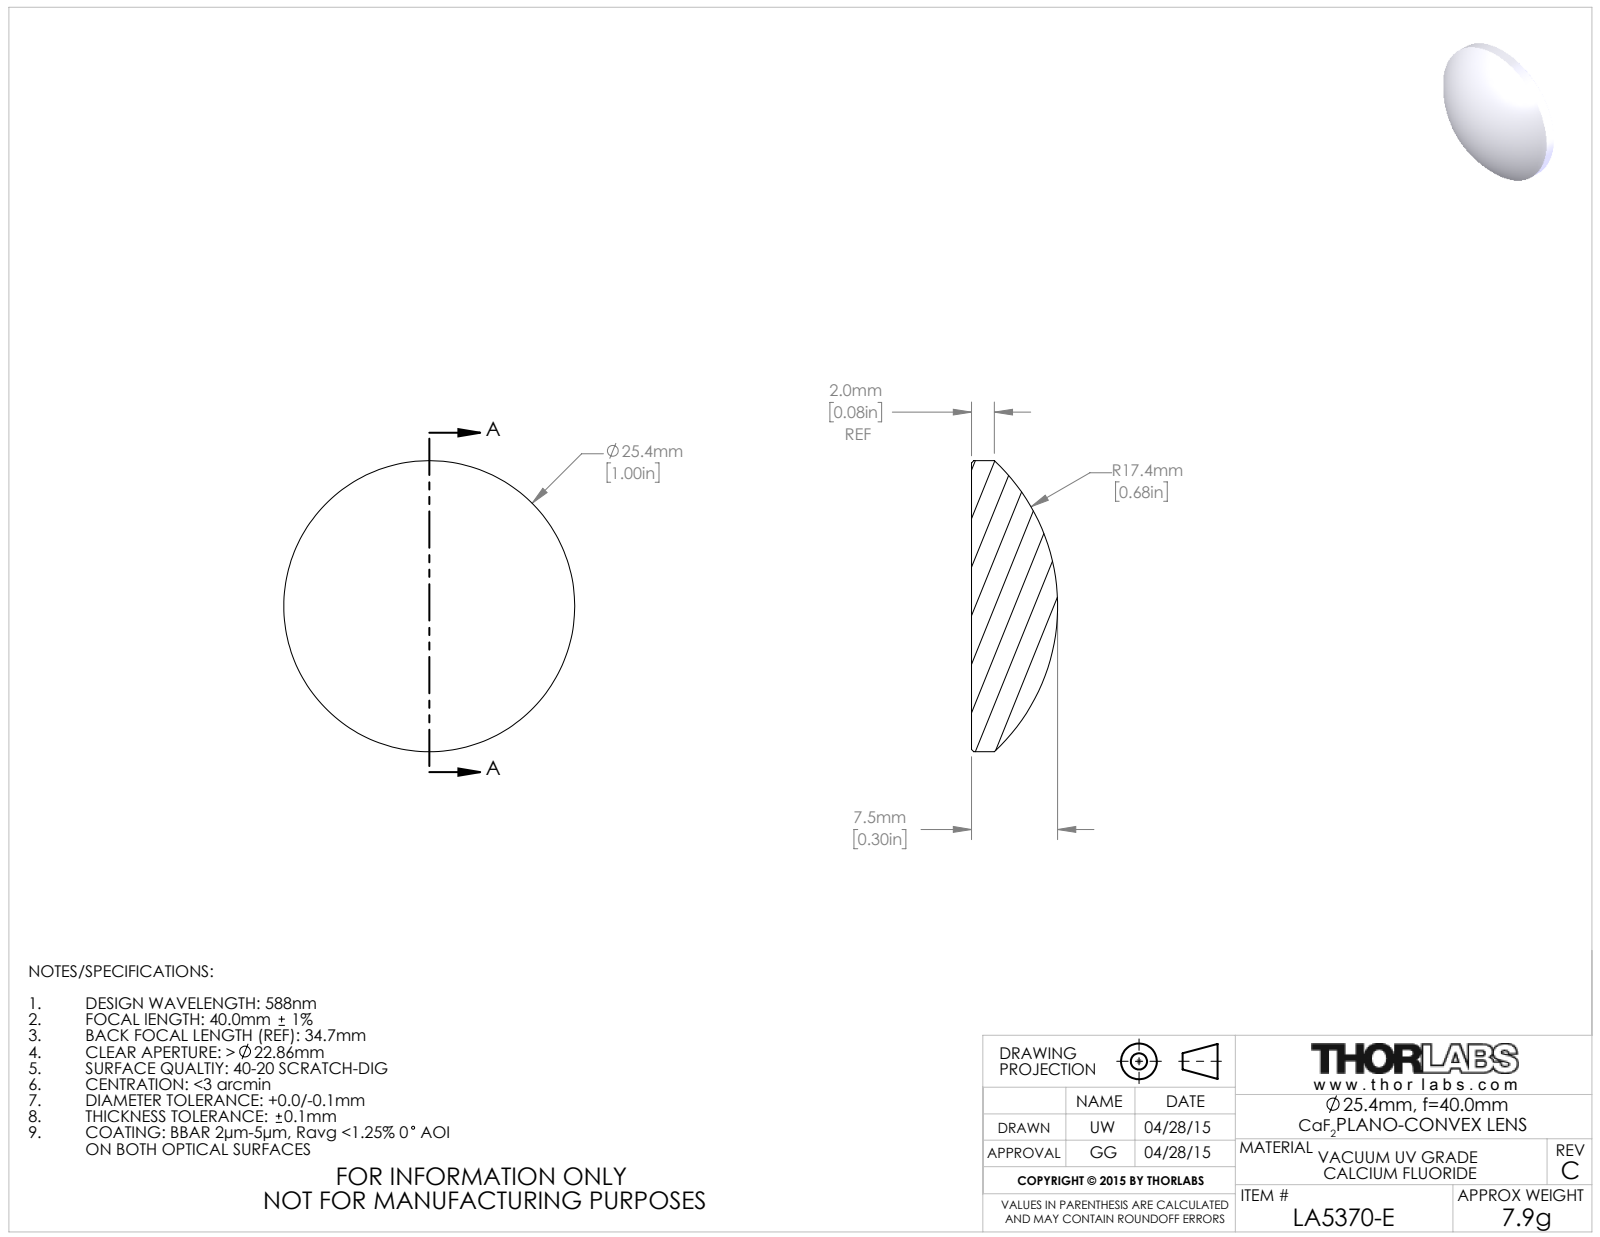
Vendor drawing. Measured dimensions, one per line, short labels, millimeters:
name: 20131-E0W
written by: SolidWorks 2018 (CONFIG_CONTROL_DESIGN)
unit: mm
bodies: 1 solid, 7 faces (1 planar, 2 cylindrical, 4 other)
size: 25.4 × 25.4 × 7.52
volume: 2 497 mm³; area: 1 259 mm²
bosses: 1× ⌀25.4
